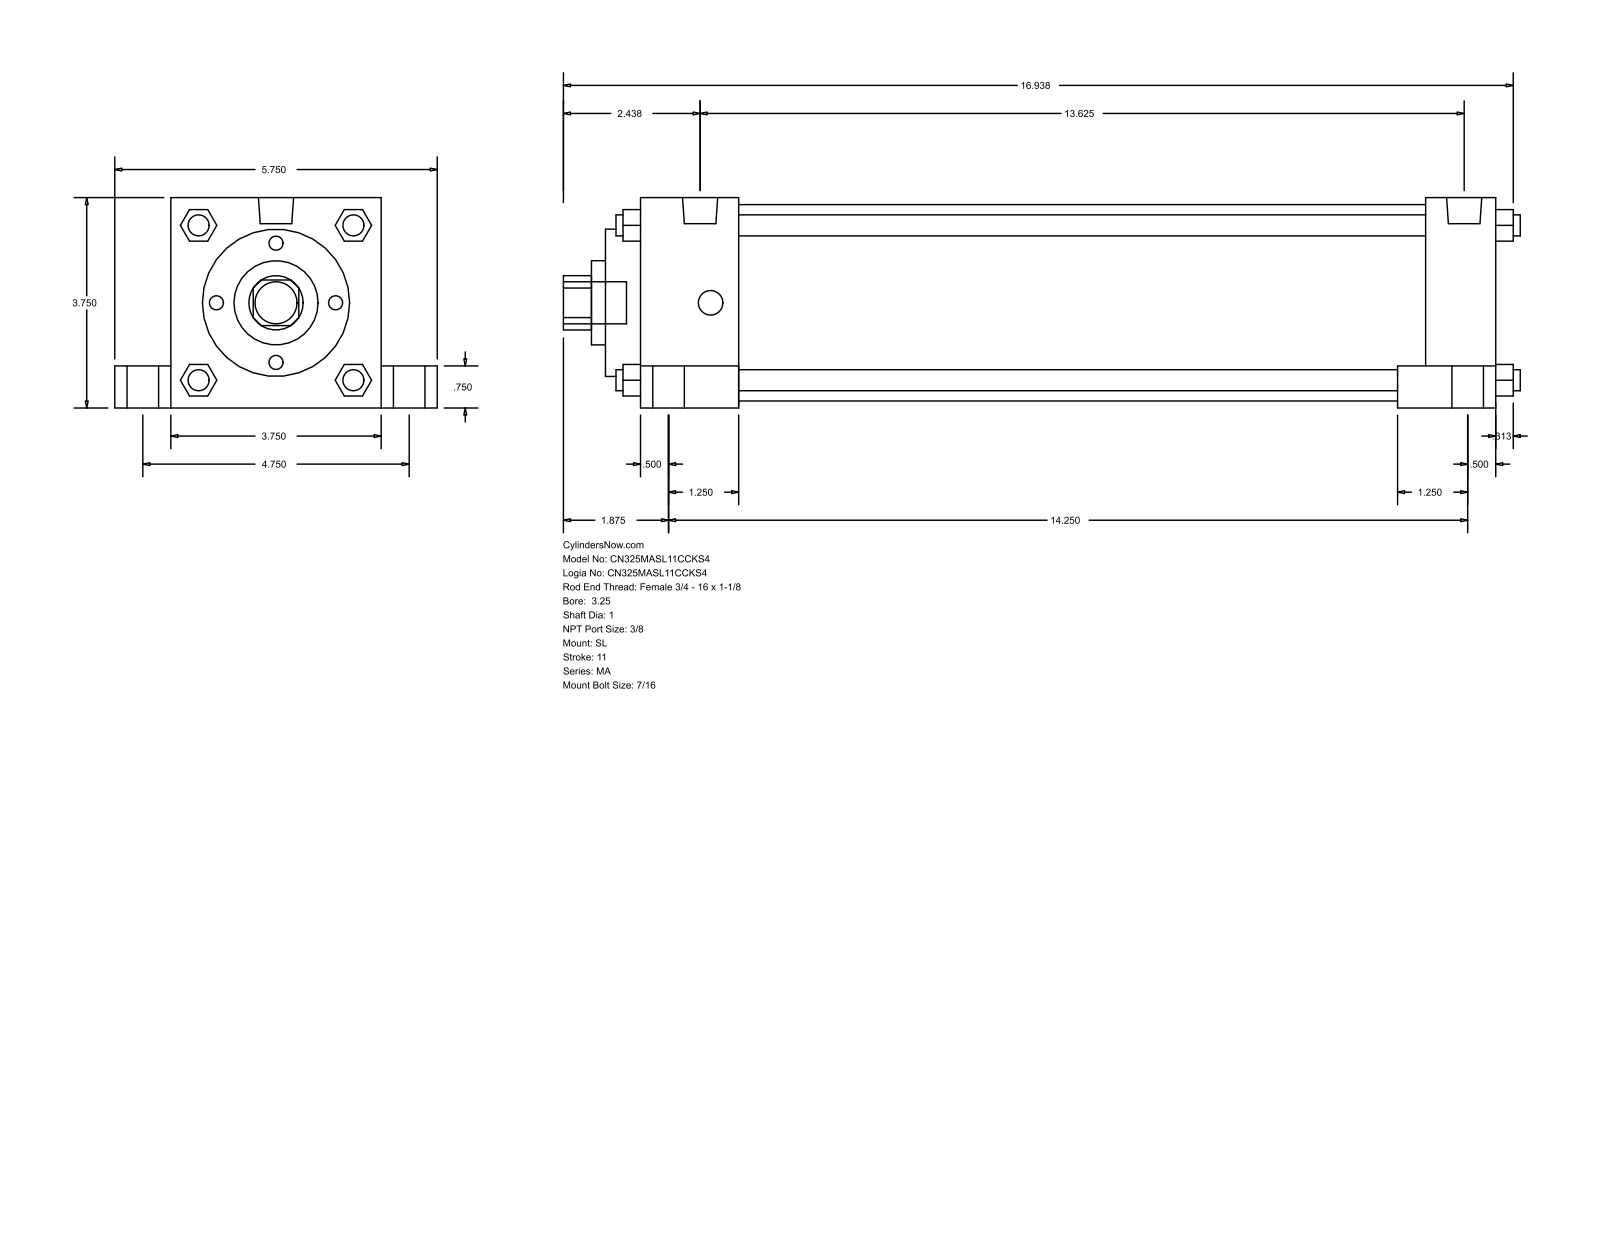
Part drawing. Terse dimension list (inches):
name: MA_SL__0325_1
written by: GSSL Pune (CONFIG_CONTROL_DESIGN)
unit: in
bodies: 0 solids, 150 faces (113 planar, 37 cylindrical, 0 other)
size: 17.063 × 5.75 × 3.75
holes: 1× ⌀1, 1× ⌀1.5, 1× ⌀2.625, 1× ⌀3.5
bosses: 4× ⌀0.813, 4× ⌀0.563, 4× ⌀0.437, 4× ⌀0.375, 2× ⌀0.627, 1× ⌀0.75
rounds: 1× R0.484
face distances: 3.75, 15.25, 0.625, 1, 4.75, 15.875, 0.75, 14, 1.25, 1.75
